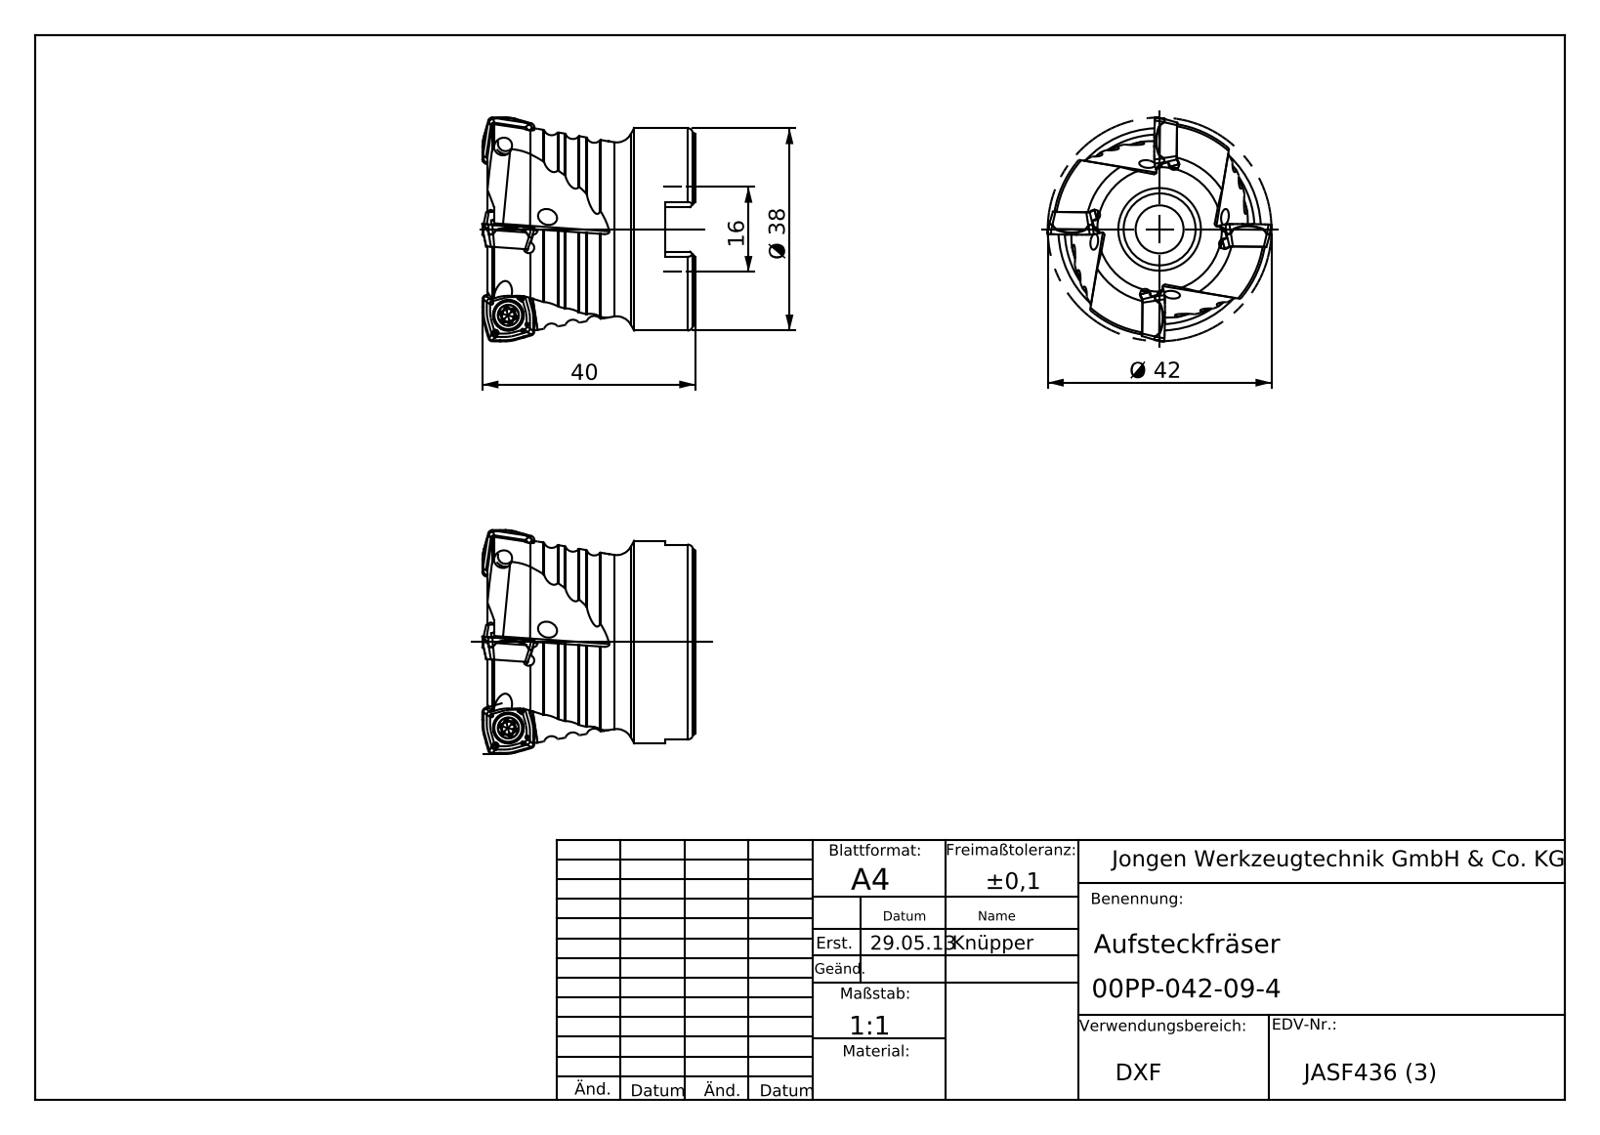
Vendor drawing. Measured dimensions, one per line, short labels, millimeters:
name: 00PP-042-09-4
written by: SolidWorks 2013 (AUTOMOTIVE_DESIGN)
unit: mm
bodies: 1 solid, 165 faces (47 planar, 34 cylindrical, 84 other)
size: 42.03 × 42.03 × 39.93
volume: 33 097 mm³; area: 9 995 mm²
holes: 4× ⌀3, 1× ⌀9, 1× ⌀13.5, 1× ⌀15.85, 1× ⌀16.15, 1× ⌀16.3
bosses: 1× ⌀38
rounds: 8× R0.5, 8× R0.8, 4× R1, 4× R2
face distances: 37.75, 5.6, 32.15, 8.4, 27, 21.4, 10.75, 20, 14.4, 7
